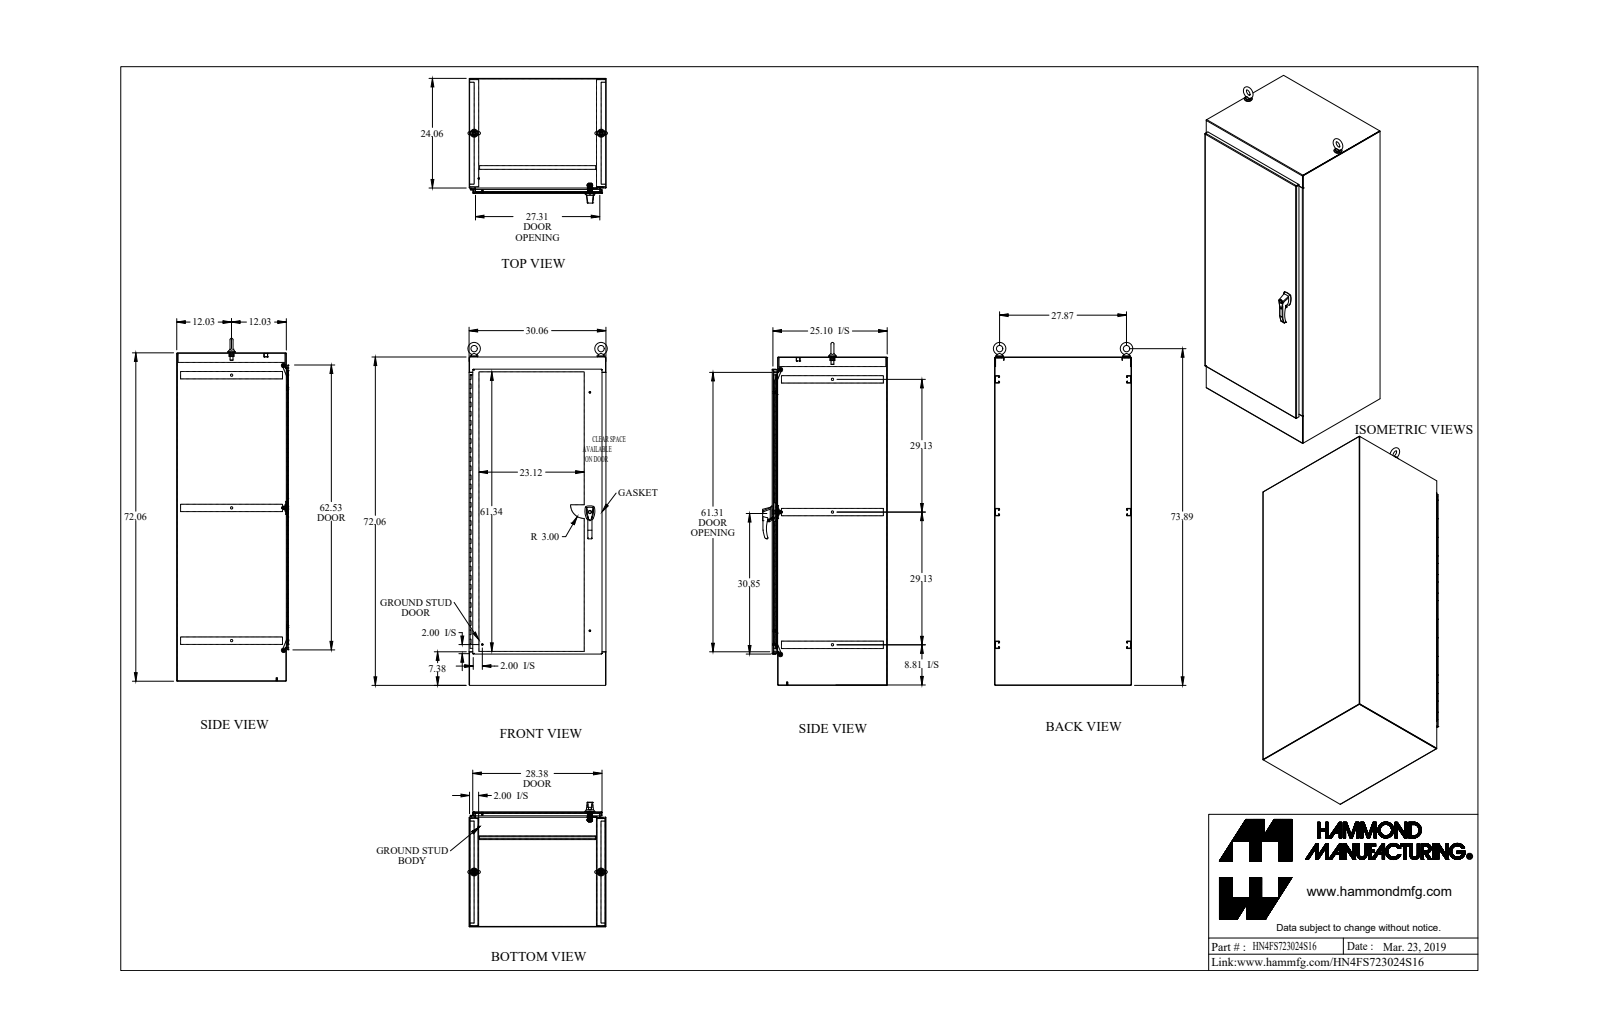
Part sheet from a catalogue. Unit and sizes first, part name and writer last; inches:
Units: inches
Overall size (bounding box): 75.256 × 30.604 × 27.362
Round holes (diameter × count): ⌀0.304 ×10, ⌀0.35 ×7, ⌀0.5 ×3, ⌀0.25 ×2, ⌀0.257 ×2, ⌀0.28 ×2, ⌀0.281 ×2, ⌀0.313 ×2, ⌀0.39 ×2, ⌀0.413 ×2, ⌀0.527 ×2, ⌀0.68 ×2
Round bosses / shafts (diameter × count): ⌀1.75 ×2, ⌀1.5 ×2, ⌀1.25 ×2, ⌀1 ×2, ⌀0.75 ×2, ⌀0.738 ×2, ⌀0.63 ×2, ⌀0.625 ×2
Partial cylindrical surfaces — rounded edges, fillets, slot ends (radius × count): R0.043 ×42, R0.138 ×36, R0.5 ×23, R0.125 ×22, R0.018 ×16, R0.06 ×15, R0.048 ×13, R0.143 ×13
Main face-to-face distances: 0.095, 25.152, 29.965, 29.87, 25.057, 25.247, 30.06, 71.965, 23.965, 1.187
Hole centre spacings: 6, 12, 18, 24, 30, 36, 42, 0.015
Volume: 1 067 in³ · Surface area: 22 414 in²
Bodies: 56 solids, 1875 faces (862 planar, 848 cylindrical, 165 other)
Part name (STEP PRODUCT): HN4FS723024S16
STEP written by: SolidWorks 2018 (AUTOMOTIVE_DESIGN)
